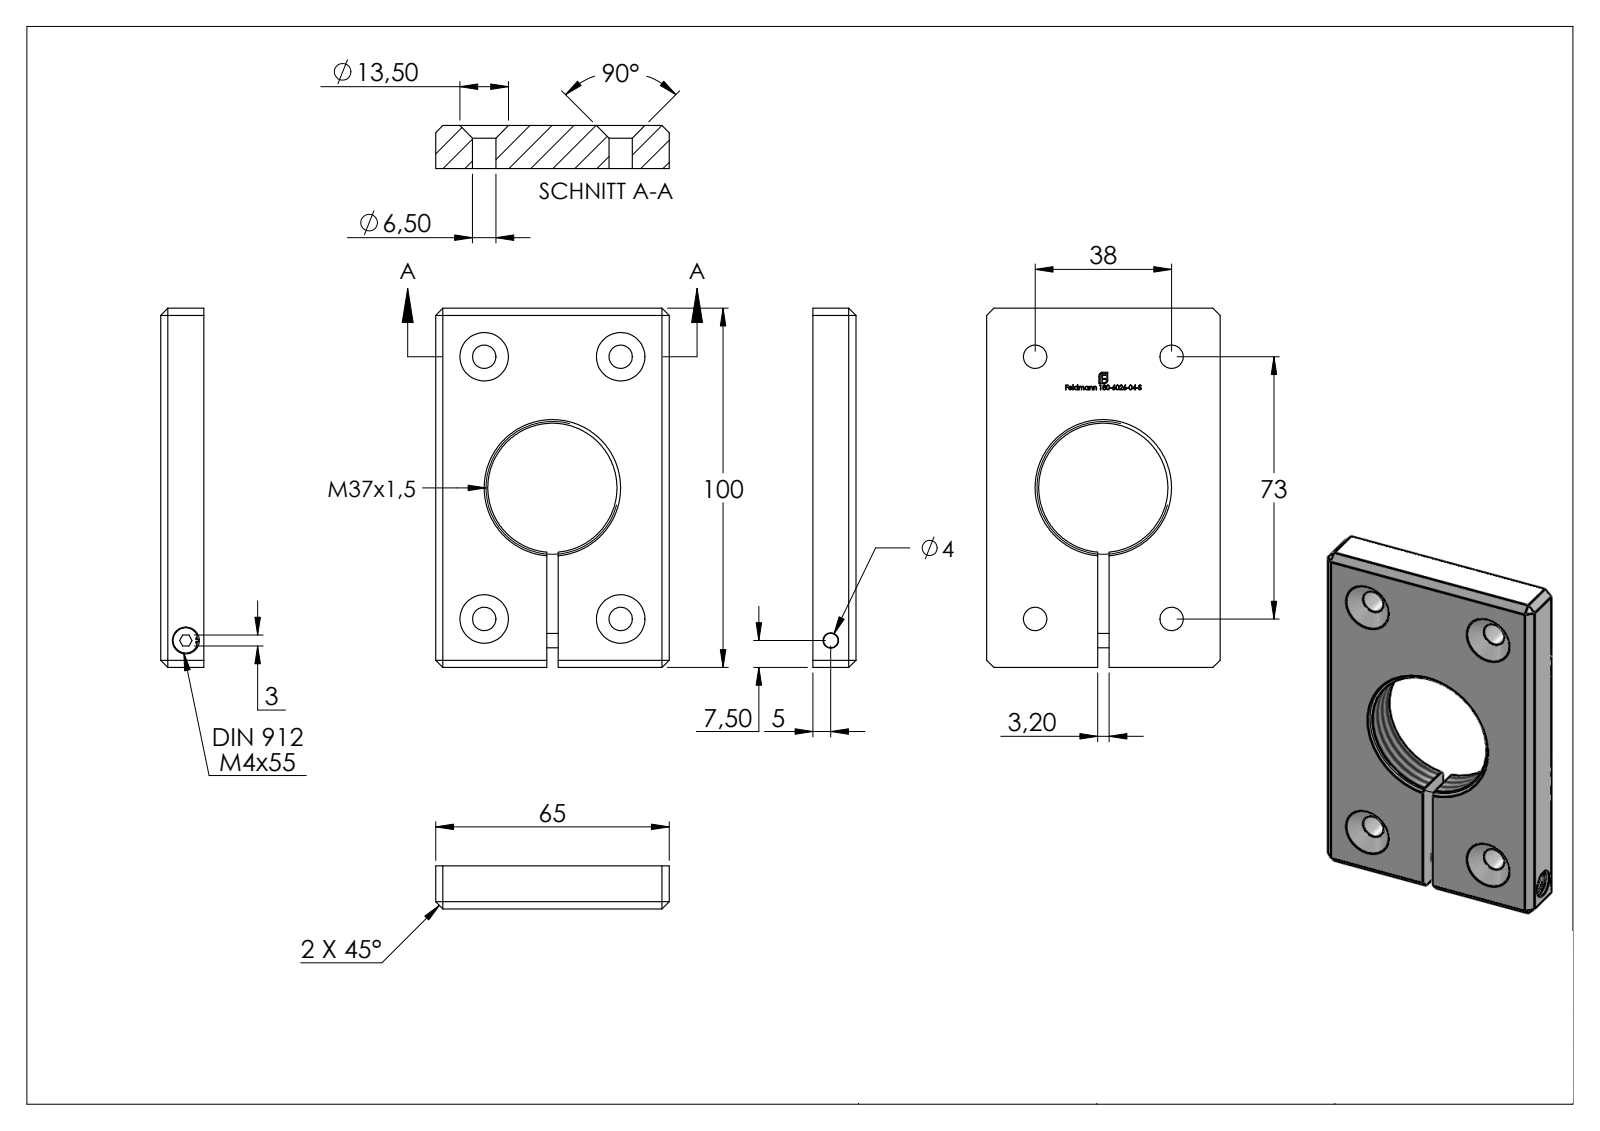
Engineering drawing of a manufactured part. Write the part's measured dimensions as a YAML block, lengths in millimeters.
part_name: "180-6026-04-S"
step_written_by: "SolidWorks 2018 (CONFIG_CONTROL_DESIGN)"
units: millimeters
bodies: {solids: 2, faces: 406, planar: 193, cylindrical: 48, other: 165}
overall_size: [100, 65, 12]
volume: 61182
surface_area: 18057
round_holes:
  - {diameter: 6.5, count: 4}
  - {diameter: 0.4, count: 2}
  - {diameter: 4.3, count: 1}
  - {diameter: 7, count: 1}
  - {diameter: 7.5, count: 1}
  - {diameter: 8.1, count: 1}
  - {diameter: 36, count: 1}
round_bosses_or_shafts:
  - {diameter: 8, count: 1}
  - {diameter: 4, count: 1}
partial_cylinders:
  - {radius: 0.1, count: 2}
  - {radius: 0.15, count: 2}
  - {radius: 0.5, count: 2}
  - {radius: 0.65, count: 2}
face_to_face_distances: [12, 65, 34.1, 30.9, 100, 3.2, 113.82, 2, 63, 32.1]
hole_center_spacings: [41.15, 3.16, 38, 73, 82.3, 1.14]
